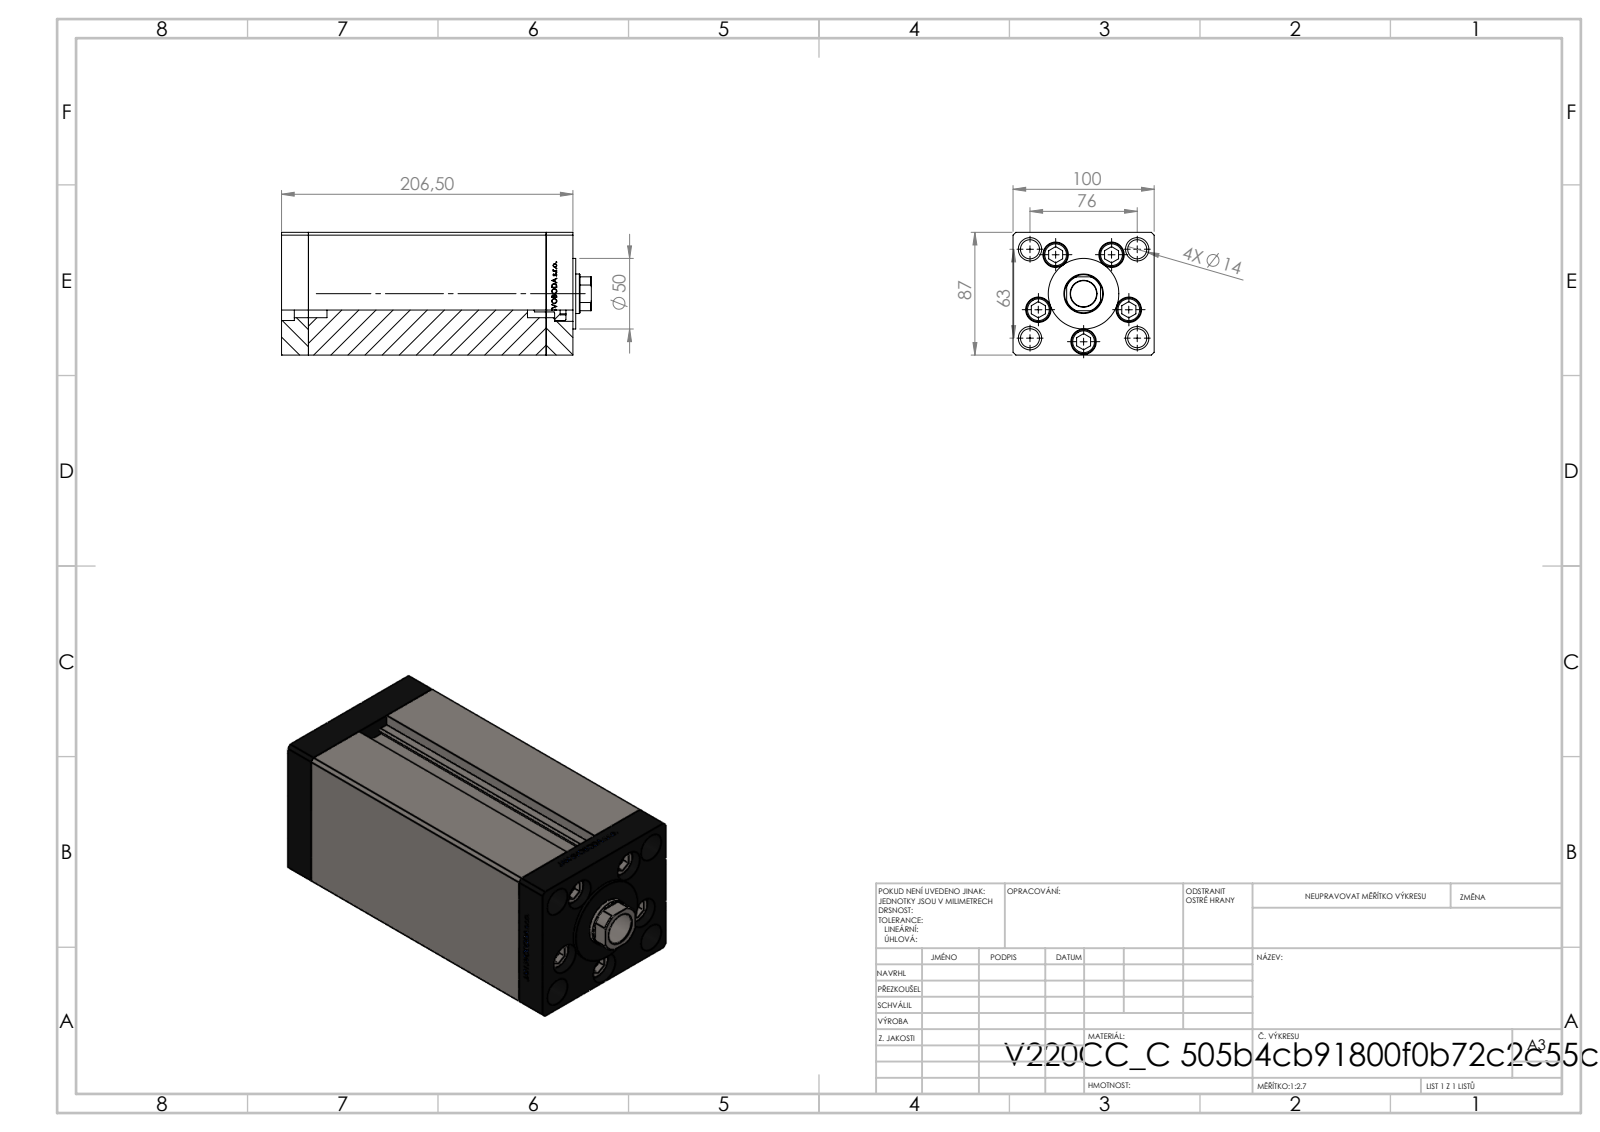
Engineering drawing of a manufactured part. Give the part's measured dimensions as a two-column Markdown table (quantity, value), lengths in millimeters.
| quantity | value |
| --- | --- |
| part name | V220C_VC_C; V220C FRONT; V220C BACK_C; V220C_C MIDDLE (+1 more) |
| STEP written by | SolidWorks 2019 (CONFIG_CONTROL_DESIGN) |
| units | millimeters |
| bodies | 13 solids, 1164 faces (542 planar, 160 cylindrical, 462 other) |
| overall size | 219.5 × 100 × 87 |
| volume | 1 470 000 mm³ |
| surface area | 245 103 mm² |
| round holes (diameter × count) | 13.5 × 9, 18 × 5, 12 × 4, 16.5 × 4, 17 × 1, 18.5 × 1, 28 × 1 |
| round bosses / shafts (diameter × count) | 8 × 5, 17 × 4, 50 × 1 |
| partial cylindrical surfaces (radius × count) | 0.93 × 2, 13.5 × 1 |
| main face-to-face distances | 100, 87, 19, 168.5, 187.5, 34.25, 206.5, 172.25, 153.25, 15.25 |
| hole center spacings | 34, 49.36, 18.59, 21.03, 38.08, 39.27, 40.83, 43.24 |
